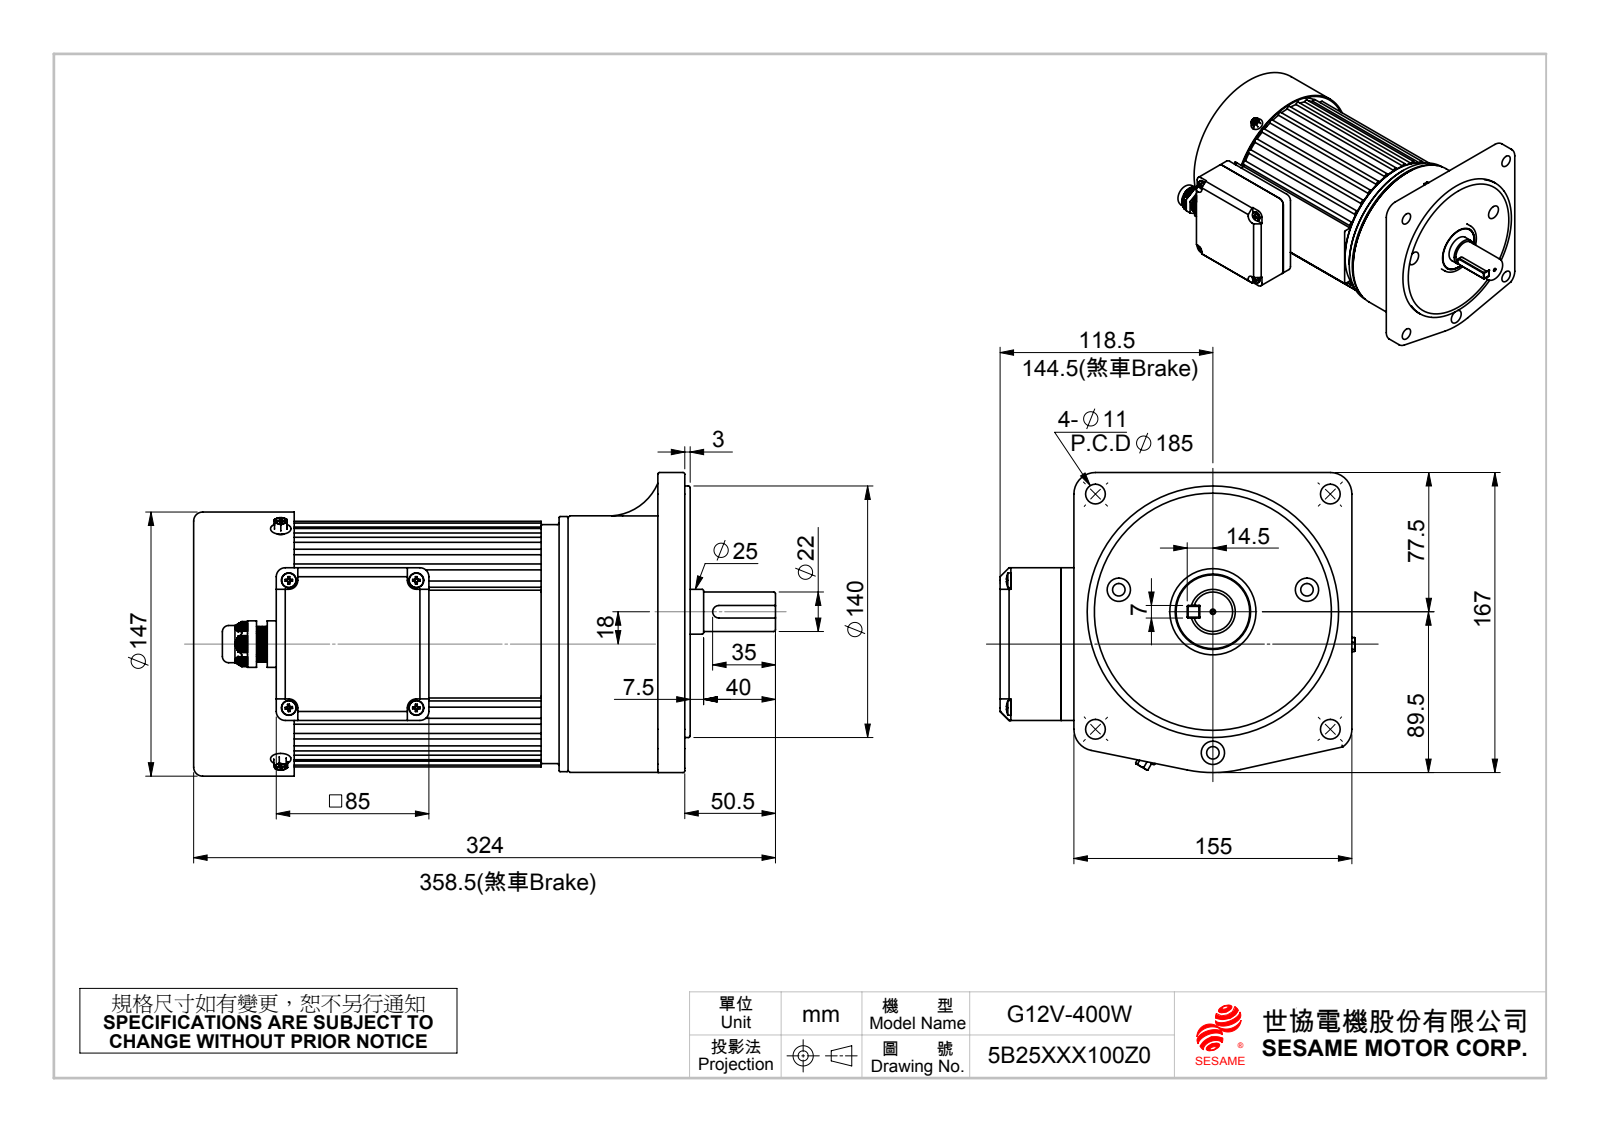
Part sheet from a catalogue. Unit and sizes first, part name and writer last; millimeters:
Units: millimetres
Overall size (bounding box): 324 × 197.61 × 169
Round holes (diameter × count): ⌀5 ×14, ⌀3.3 ×9, ⌀11 ×7, ⌀6 ×5, ⌀8 ×4, ⌀7 ×3, ⌀13 ×3, ⌀2 ×1, ⌀10.8 ×1, ⌀16.5 ×1, ⌀24.95 ×1, ⌀42 ×1
Round bosses / shafts (diameter × count): ⌀8.3 ×4, ⌀4 ×4, ⌀5 ×2, ⌀147 ×1, ⌀142.8 ×1, ⌀142 ×1, ⌀140 ×1, ⌀133 ×1
Partial cylindrical surfaces — rounded edges, fillets, slot ends (radius × count): R1 ×53, R1.85 ×31, R0.5 ×24, R2 ×8, R5 ×8, R2.75 ×6, R2.55 ×4, R3.55 ×4
Main face-to-face distances: 65.5, 160, 44, 140, 20, 212.5, 53.5, 9.5, 5.5, 149.5
Hole centre spacings: 45, 63.67, 71, 60.5, 11, 11.5, 14.6, 14.79
Volume: 4 071 000 mm³ · Surface area: 427 753 mm²
Bodies: 19 solids, 2707 faces (833 planar, 825 cylindrical, 1049 other)
Part name (STEP PRODUCT): 400W風扇蓋145x56／缺口70(直角); G12-400C1; 成品-塑膠T盒; 出線盒下蓋 (+8 more)
STEP written by: SolidWorks 2010 (CONFIG_CONTROL_DESIGN)
